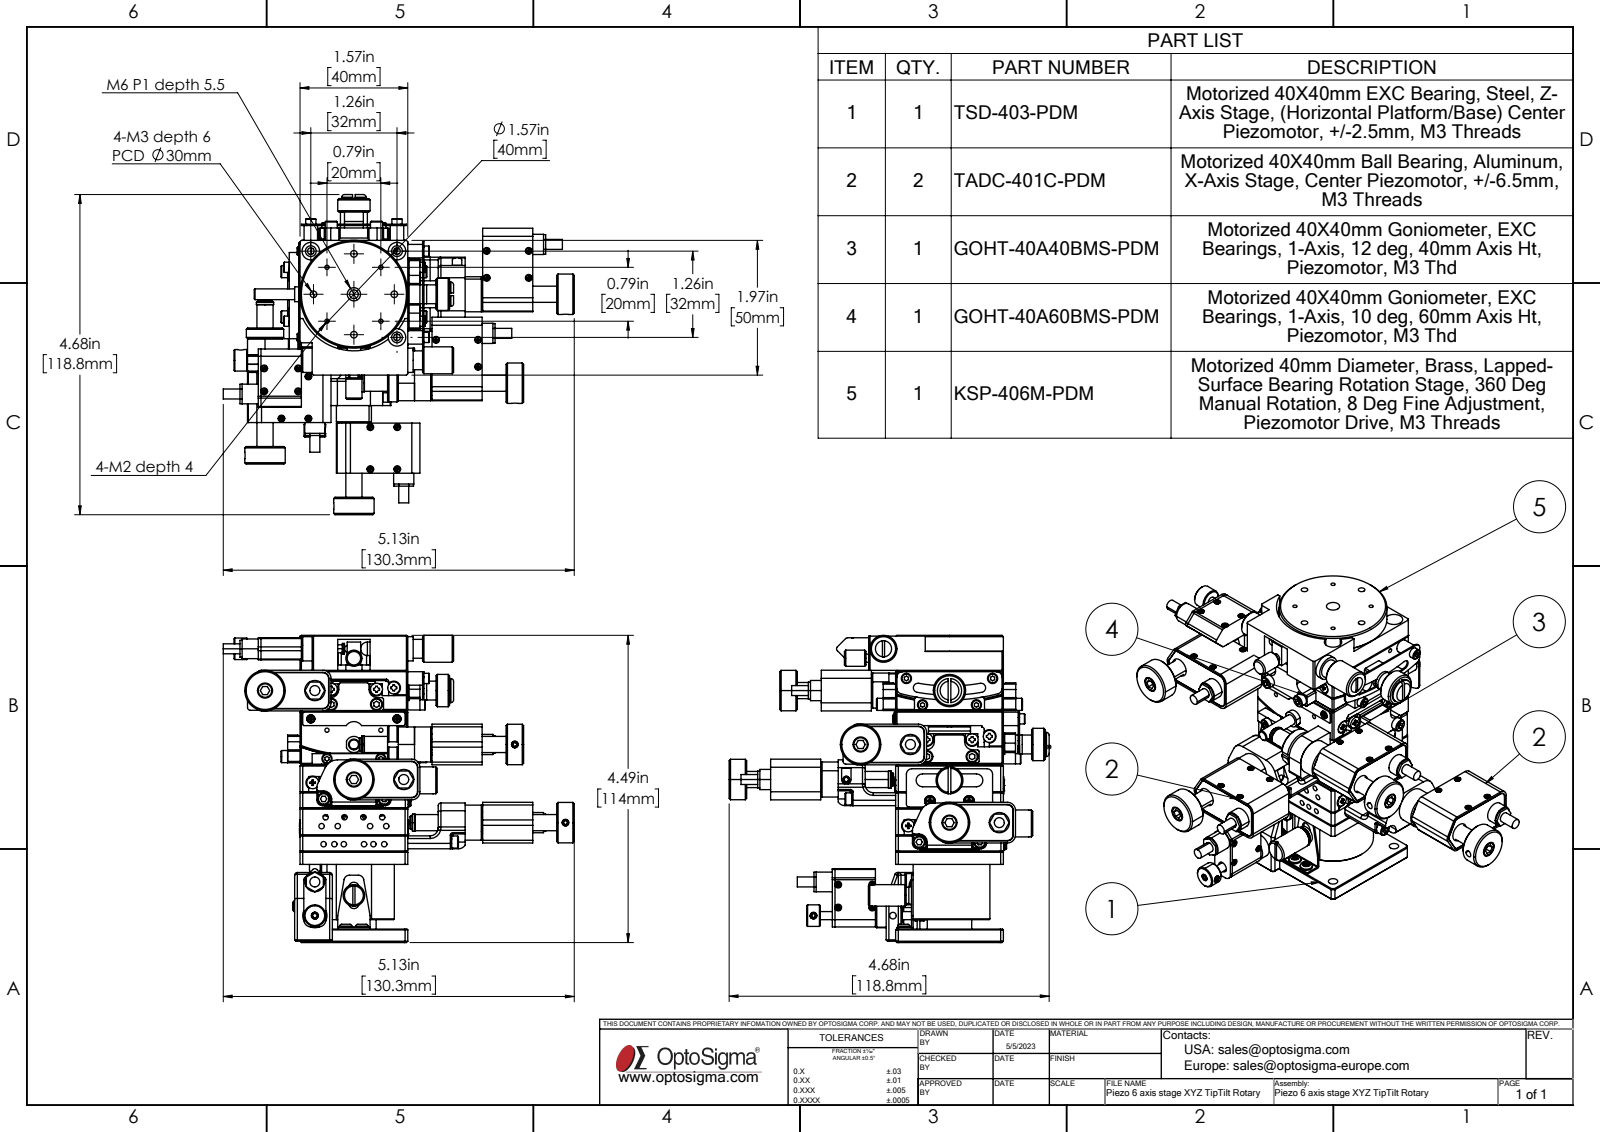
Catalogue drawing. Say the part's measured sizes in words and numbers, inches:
The part is named "PDM6ACT-M02-20001-S02; PDM-6.5ACT; GOHT40A40BSEE-M02-08001-S11; PDM13ACT-M02-20001-P01 (+8 more)". Its 3-D file was written by "SolidWorks 2023 (AUTOMOTIVE_DESIGN)". It is 39 solids with 8229 faces: 3684 planar, 1876 cylindrical and 2669 other. Overall it measures 5.13 by 4.677 by 4.488 inches. Its volume is 7.914 cubic inches and its surface area 212.8 square inches. Round holes: 33 of diameter 0.059, 23 of diameter 0.079, 20 of diameter 0.055, 18 of diameter 0.098, 12 of diameter 0.043, 11 of diameter 0.197, 11 of diameter 0.236, 8 of diameter 0.098, 6 of diameter 0.043, 4 of diameter 0.062, 4 of diameter 0.102, 4 of diameter 0.138. Round bosses or shafts: 65 of diameter 0.079, 48 of diameter 0.15, 32 of diameter 0.177, 24 of diameter 0.055, 18 of diameter 0.118, 16 of diameter 0.098, 8 of diameter 0.197, 6 of diameter 0.315. Partial cylindrical surfaces (rounded edges, fillets, slot ends): 43 of radius 0.039, 40 of radius 0.031, 35 of radius 0.079, 35 of radius 0.118, 24 of radius 0.02, 8 of radius 0.098, 6 of radius 0.197, 5 of radius 0.059. The main face-to-face distances are 0.63, 1.575, 0.197, 0.276, 0.787, 1.654, 1.26, 2.008, 2.047, 1.417. The hole center spacings are 0.63, 1.26, 0.169, 0.42, 0.461, 0.635, 0.652, 0.676.
